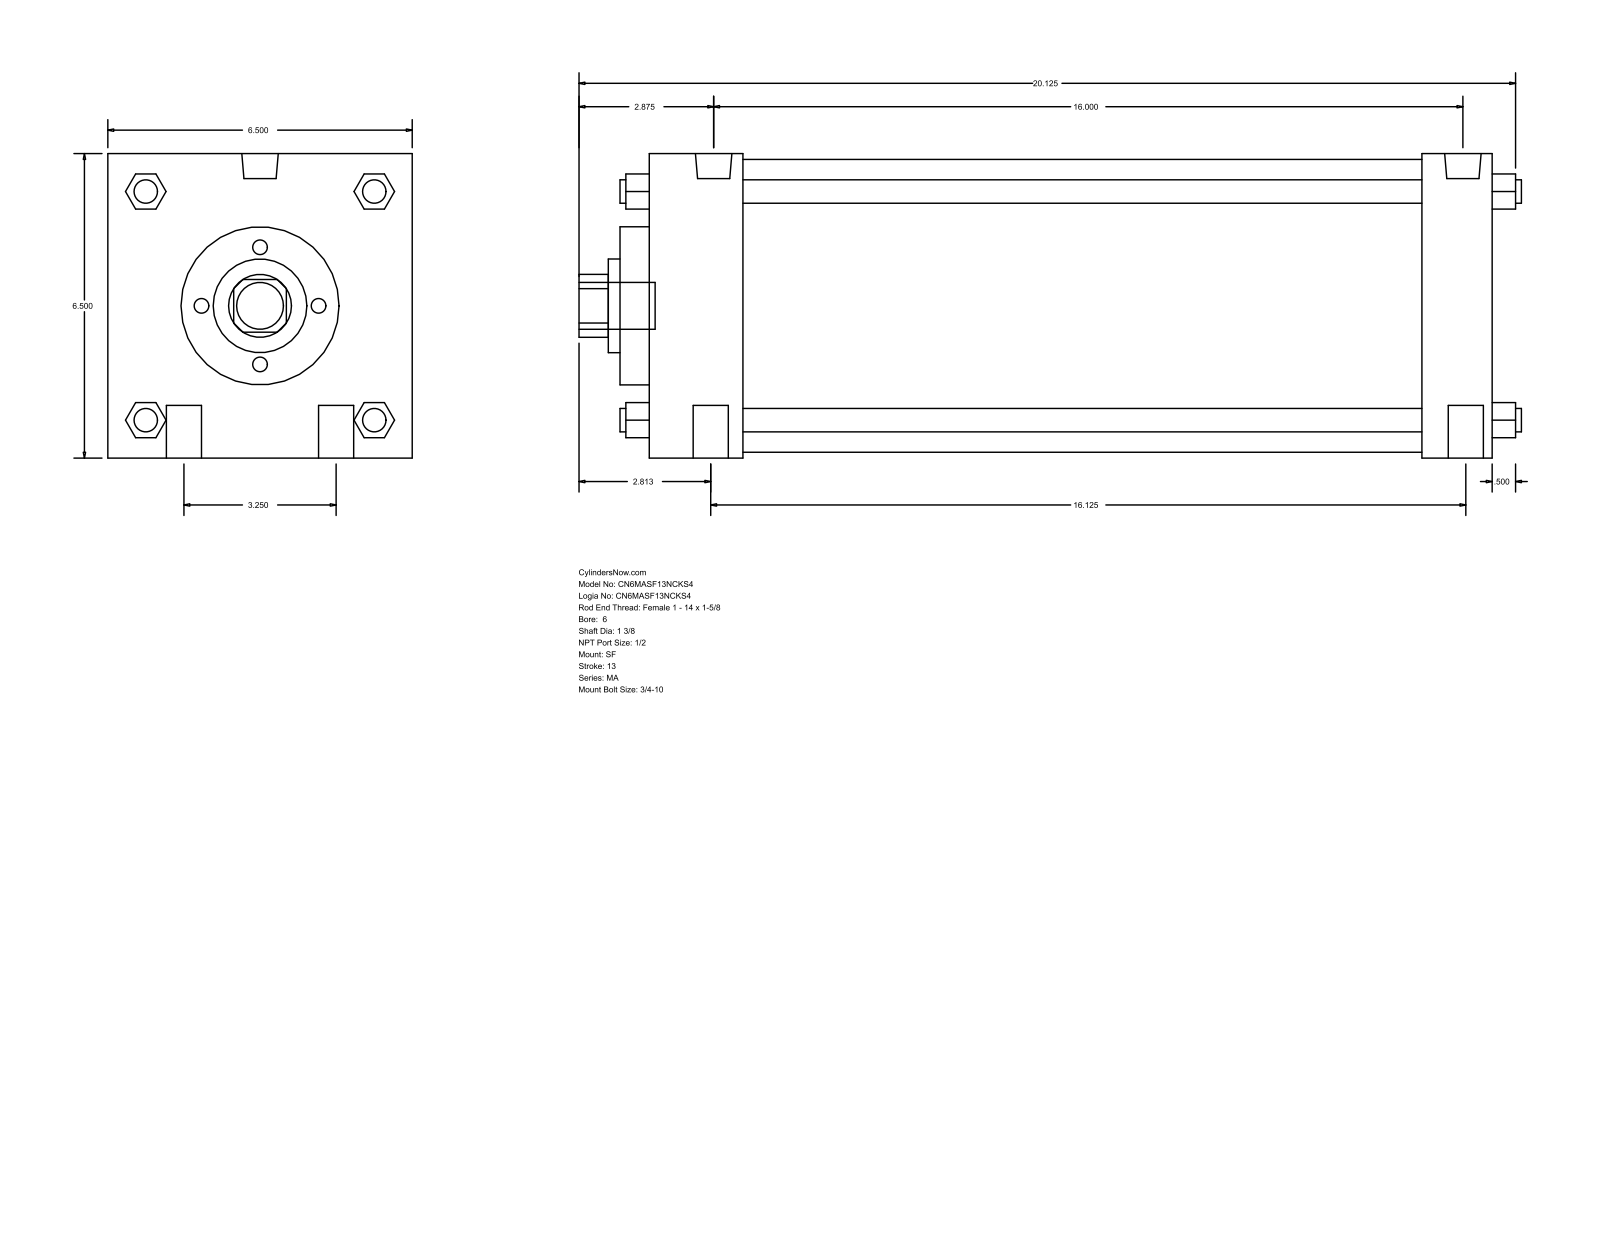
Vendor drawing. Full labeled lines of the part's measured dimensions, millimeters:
Part name (STEP PRODUCT): MA_SF__0600_1.375
STEP written by: GSSL Pune (CONFIG_CONTROL_DESIGN)
Units: millimetres
Bodies: 0 solids, 126 faces (95 planar, 31 cylindrical, 0 other)
Overall size (bounding box): 511.18 × 165.1 × 165.1
Round holes (diameter × count): ⌀34.92 ×1, ⌀50.8 ×1, ⌀85.72 ×1, ⌀158.75 ×1
Round bosses / shafts (diameter × count): ⌀19.05 ×4, ⌀12.7 ×4, ⌀19.77 ×2, ⌀17.46 ×2, ⌀25.4 ×1
Partial cylindrical surfaces — rounded edges, fillets, slot ends (radius × count): R17.06 ×1
Main face-to-face distances: 165.1, 457.2, 419.1, 50.8, 38.1, 368.3, 406.4, 15.87, 66.67, 434.97
